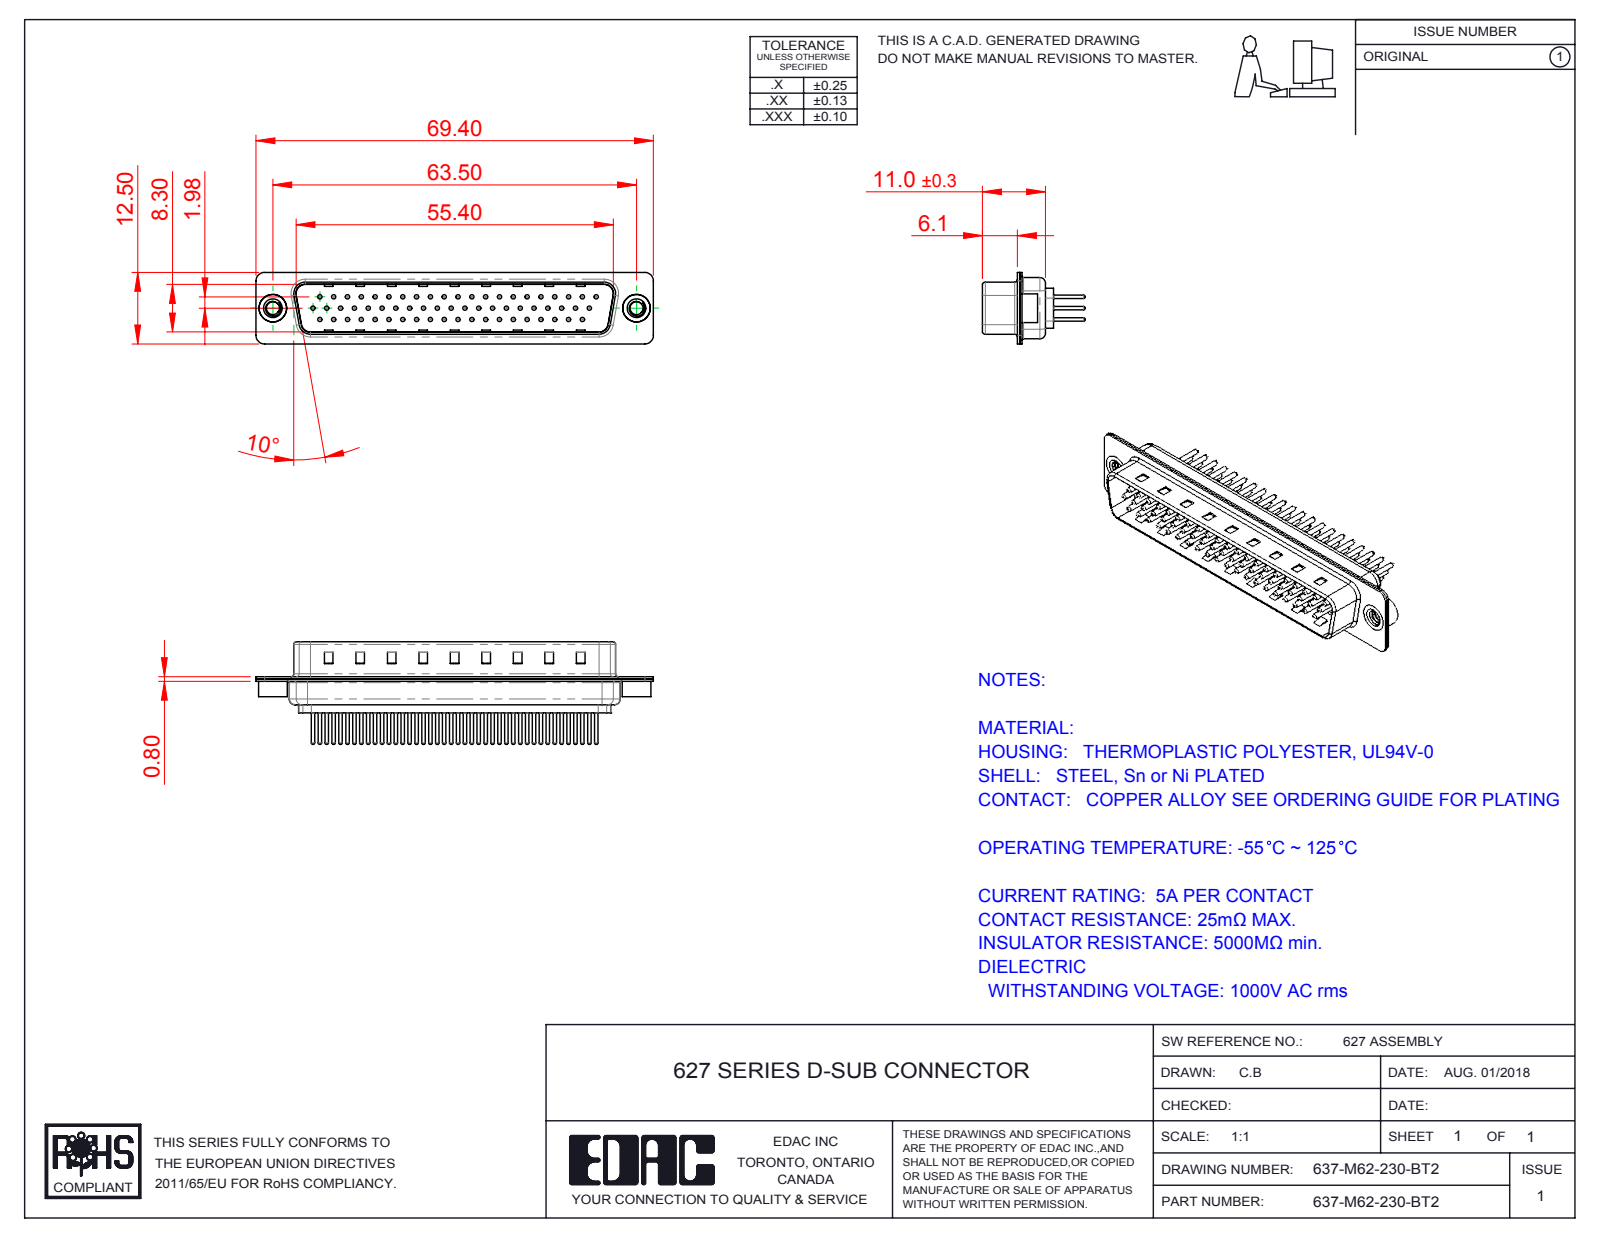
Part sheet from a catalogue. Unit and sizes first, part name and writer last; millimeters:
Units: millimetres
Overall size (bounding box): 69.4 × 17.9 × 12.5
Round holes (diameter × count): ⌀0.75 ×62, ⌀1.6 ×62, ⌀2 ×62, ⌀2.26 ×2, ⌀4 ×2, ⌀4.8 ×2
Round bosses / shafts (diameter × count): ⌀1.5 ×62, ⌀0.6 ×62, ⌀5 ×2, ⌀4.9 ×2
Partial cylindrical surfaces — rounded edges, fillets, slot ends (radius × count): R1.5 ×16, R2 ×12, R0.5 ×8, R1.6 ×8, R0.25 ×4, R0.6 ×4, R0.65 ×4, R0.9 ×4
Main face-to-face distances: 0.4, 0.8, 9.5, 9.1, 8.7, 9.9, 0.75, 0.35, 5.9, 1.2
Hole centre spacings: 7.24, 2.32, 2.41, 4.13, 9.65, 4.83, 14.48, 11.04
Volume: 3 918 mm³ · Surface area: 11 413 mm²
Bodies: 67 solids, 2706 faces (637 planar, 1009 cylindrical, 1060 other)
Part name (STEP PRODUCT): 637M Contact Row 3_30; 637M Shell Front_62 Contacts; 637M 4-40 Threaded Rivet; 637M Shell Rear_62 Contacts (+4 more)
STEP written by: SolidWorks 2016 (CONFIG_CONTROL_DESIGN)
